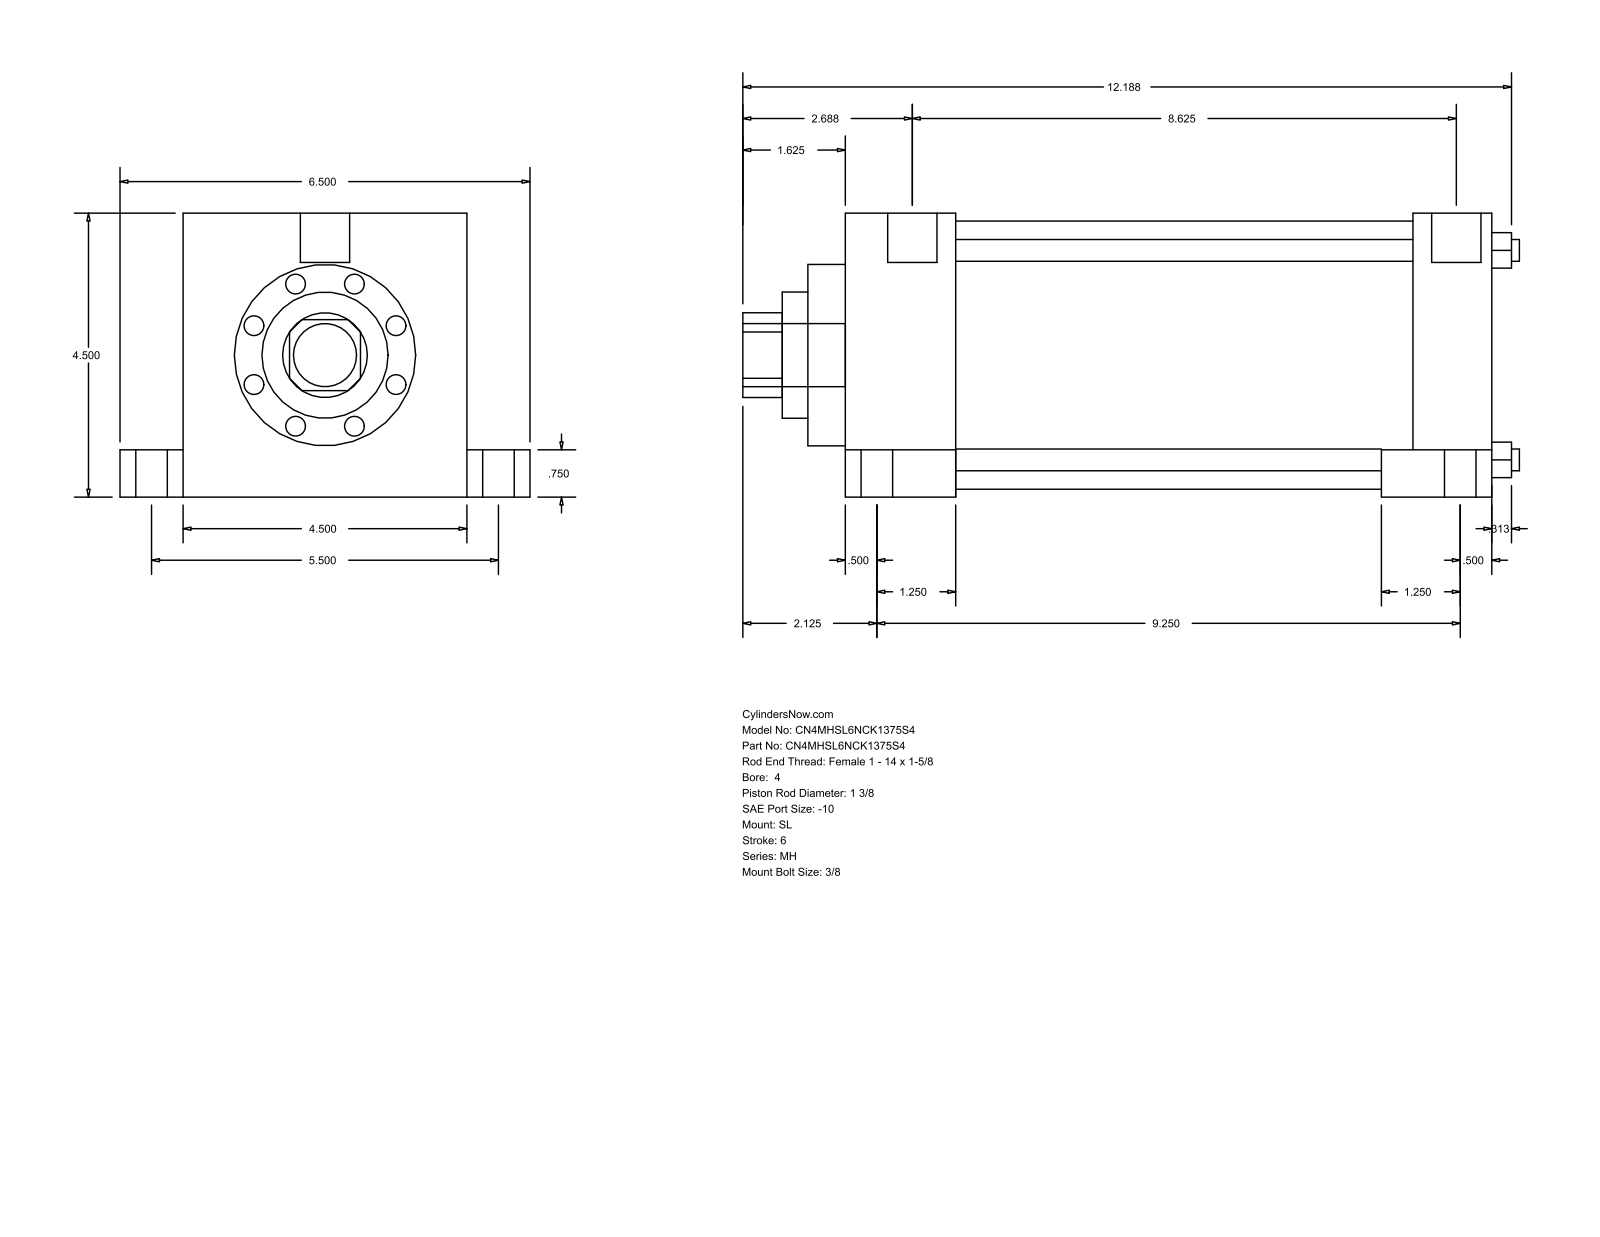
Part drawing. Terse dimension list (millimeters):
name: MH_SL__0400_1.375
written by: GSSL Pune (CONFIG_CONTROL_DESIGN)
unit: mm
bodies: 0 solids, 110 faces (77 planar, 33 cylindrical, 0 other)
size: 312.74 × 165.1 × 114.3
holes: 4× ⌀8.76, 1× ⌀34.92, 1× ⌀50.8, 1× ⌀73.03, 1× ⌀107.95
bosses: 4× ⌀19.05, 4× ⌀12.7, 4× ⌀8.73, 2× ⌀19.84, 1× ⌀25.4
rounds: 1× R17.06
face distances: 114.3, 260.35, 44.45, 215.9, 228.61, 184.16, 31.74, 25.4, 139.7, 19.05
hole spacings: 59.62, 84.32, 119.25
